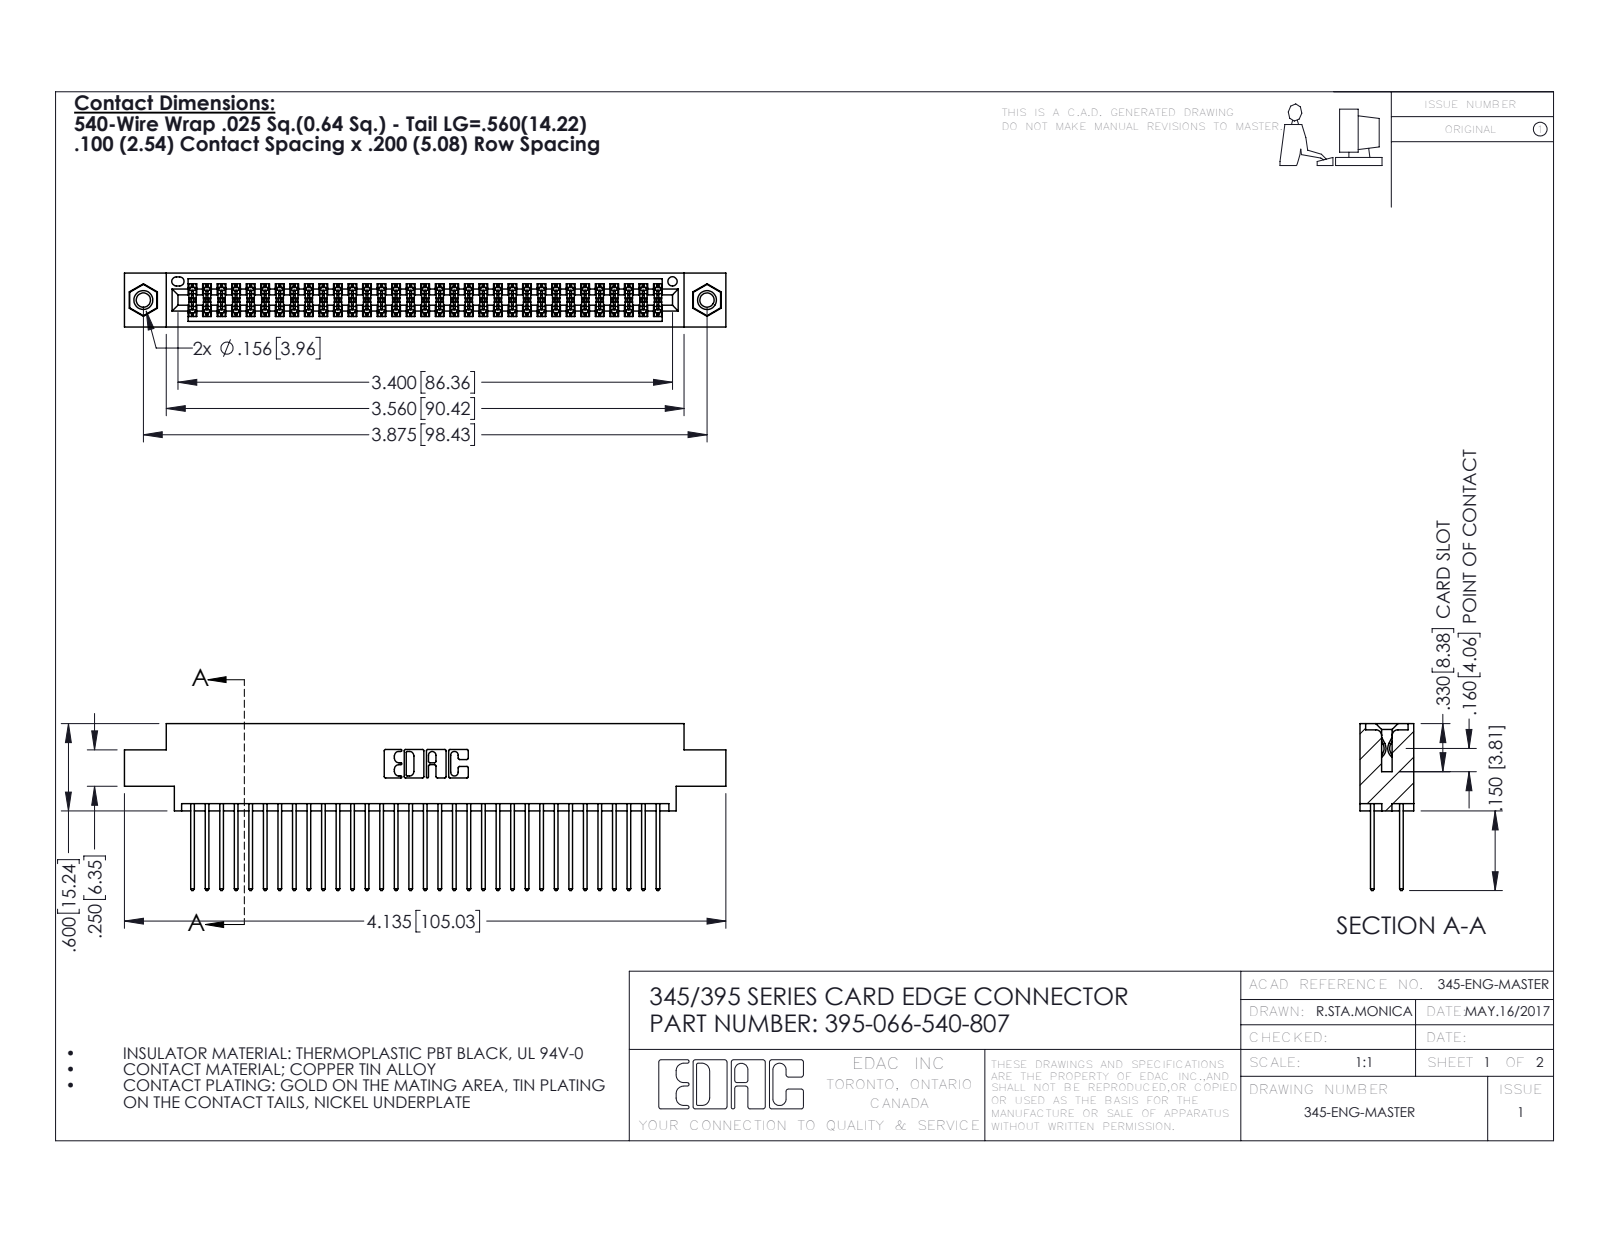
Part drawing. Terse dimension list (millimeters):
name: 345-292-001_345-293-140; 345 Part_0.170 Offset - 0.156 Dia-TI; 345-250-001_345-250-005-103; 395-066-540-807
written by: SolidWorks 2016 (CONFIG_CONTROL_DESIGN)
unit: mm
bodies: 69 solids, 3490 faces (2294 planar, 1180 cylindrical, 16 other)
size: 105 × 29.1 × 9.4
volume: 10 200 mm³; area: 16 300 mm²
holes: 2× ⌀2.5, 2× ⌀3.2, 2× ⌀4, 1× ⌀1.6
bosses: 2× ⌀3.9
rounds: 99× R0.2, 66× R0.3, 22× R0.3, 6× R0.2, 6× R0.8, 3× R0.7, 2× R0.4, 2× R0.5
face distances: 1.8, 7.6, 5.1, 2.5, 6.9, 0.6, 9.4, 5.7, 4.4, 3.8
hole spacings: 6.9, 92.5, 98.4
